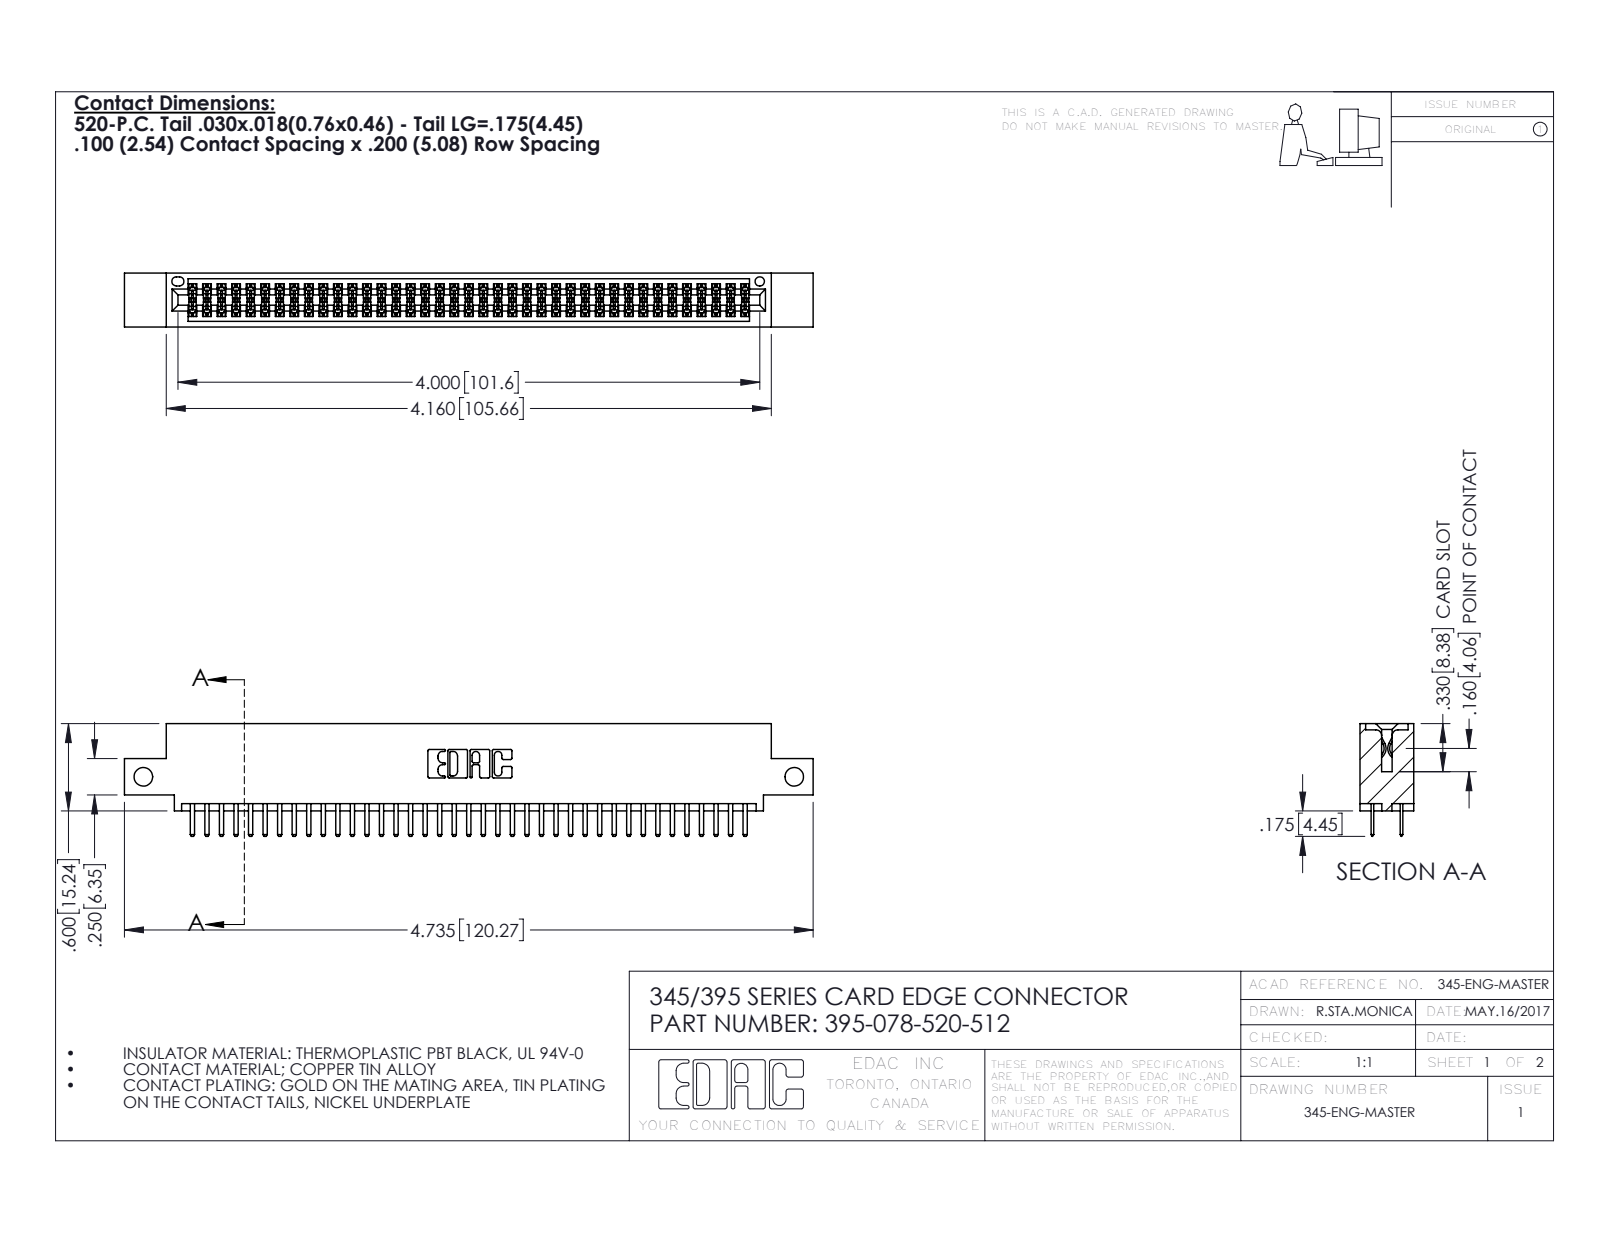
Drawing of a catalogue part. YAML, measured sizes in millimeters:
part_name: "395-078-520-512; 345 Part_0.110 Offset - Side Mount; 345-292-001_345-293-120"
step_written_by: "SolidWorks 2016 (CONFIG_CONTROL_DESIGN)"
units: millimeters
bodies: {solids: 79, faces: 4342, planar: 2814, cylindrical: 1528, other: 0}
overall_size: [120.3, 19.7, 9.4]
volume: 11500
surface_area: 16770
round_holes:
  - {diameter: 3.3, count: 2}
  - {diameter: 1.6, count: 1}
partial_cylinders:
  - {radius: 0.2, count: 117}
  - {radius: 0.3, count: 82}
  - {radius: 0.3, count: 22}
  - {radius: 0.2, count: 6}
  - {radius: 0.8, count: 6}
  - {radius: 0.7, count: 3}
  - {radius: 0.4, count: 2}
  - {radius: 0.5, count: 2}
face_to_face_distances: [7.6, 1.8, 5.1, 9.4, 2.5, 6.9, 0.6, 5.7, 0.6, 1.8]
hole_center_spacings: [113.7]
